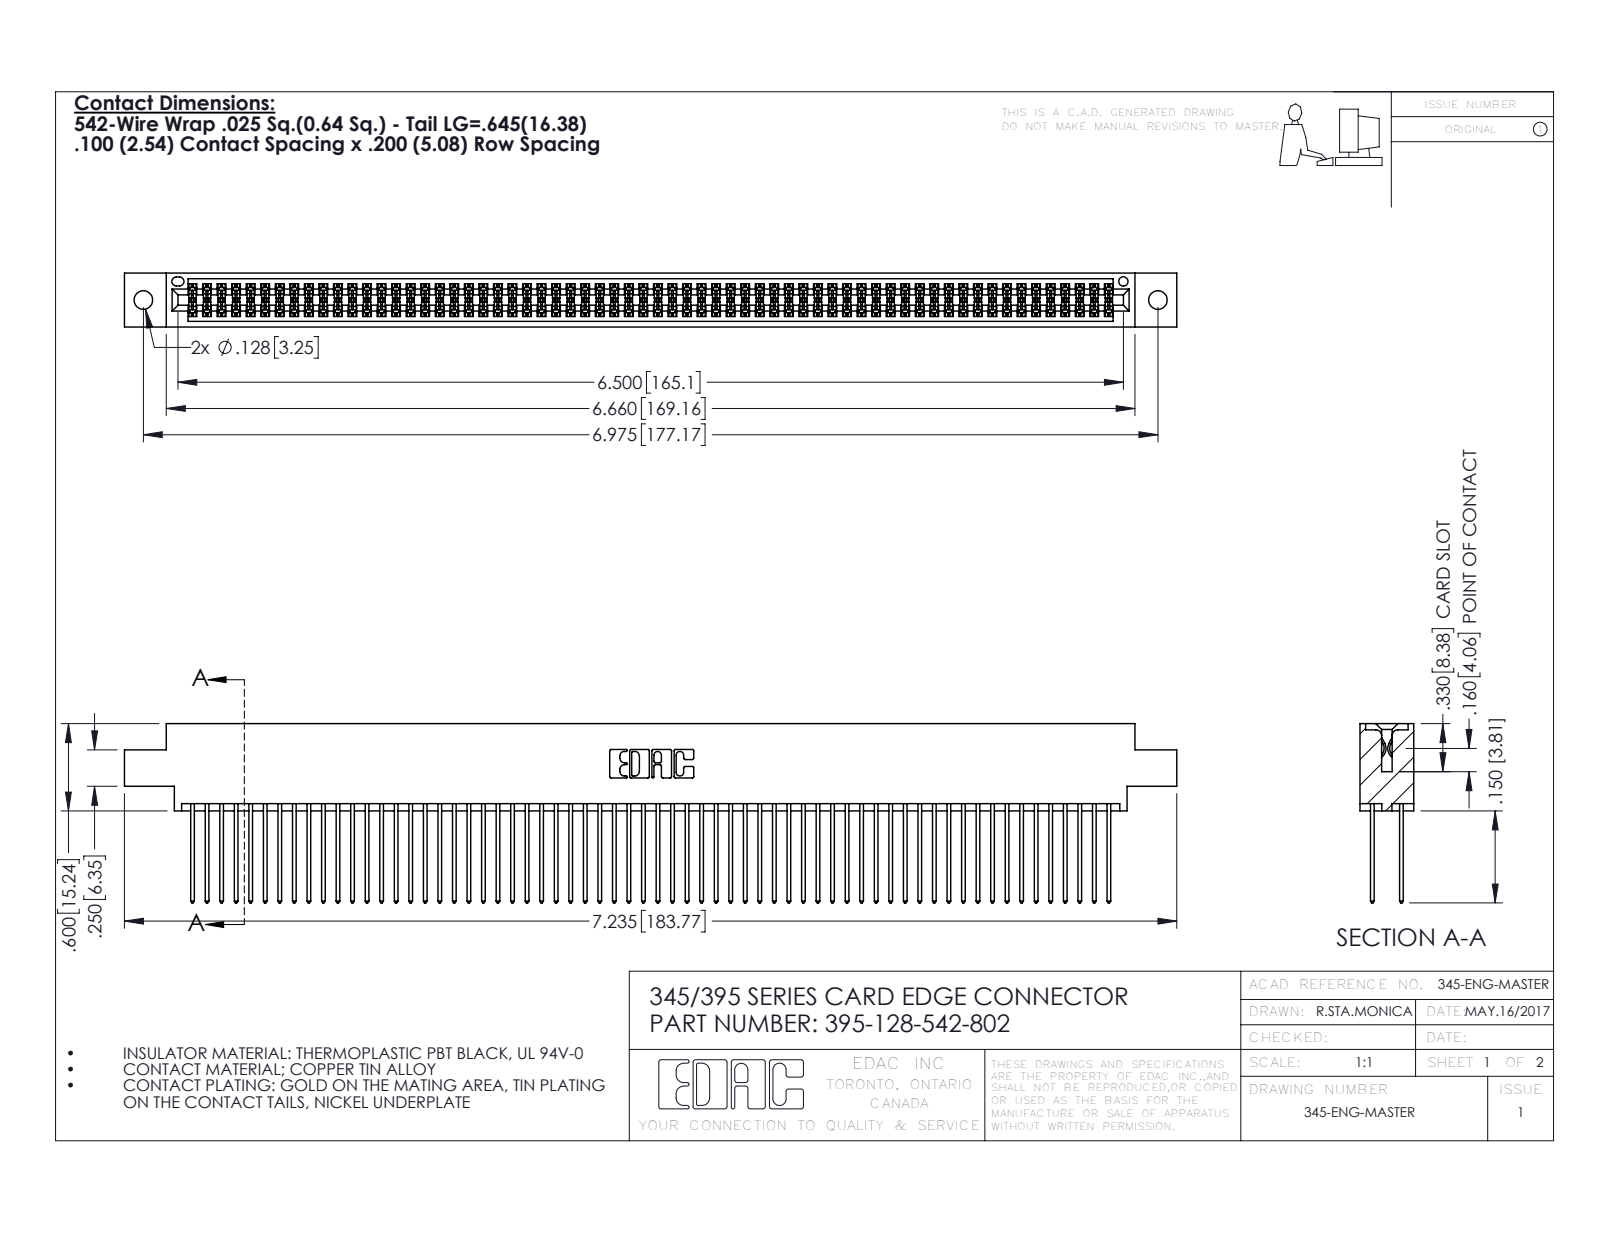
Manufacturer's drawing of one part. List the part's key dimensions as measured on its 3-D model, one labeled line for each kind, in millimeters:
Part name (STEP PRODUCT): 345 Part_0.170 Offset - 0.128 Dia; 395-128-542-802; 345-292-001_345-293-142
STEP written by: SolidWorks 2016 (CONFIG_CONTROL_DESIGN)
Units: millimetres
Bodies: 129 solids, 6530 faces (4308 planar, 2222 cylindrical, 0 other)
Overall size (bounding box): 183.8 × 31.3 × 9.4
Volume: 18 500 mm³ · Surface area: 30 430 mm²
Round holes (diameter × count): ⌀3.3 ×2, ⌀1.6 ×1
Partial cylindrical surfaces — rounded edges, fillets, slot ends (radius × count): R0.2 ×192, R0.3 ×128, R0.3 ×22, R0.2 ×6, R0.8 ×6, R0.7 ×3, R0.4 ×2, R0.5 ×2
Main face-to-face distances: 1.8, 7.6, 5.1, 2.5, 6.9, 0.6, 9.4, 5.7, 4.4, 3.8
Hole centre spacings: 6.9, 171.2, 177.2
